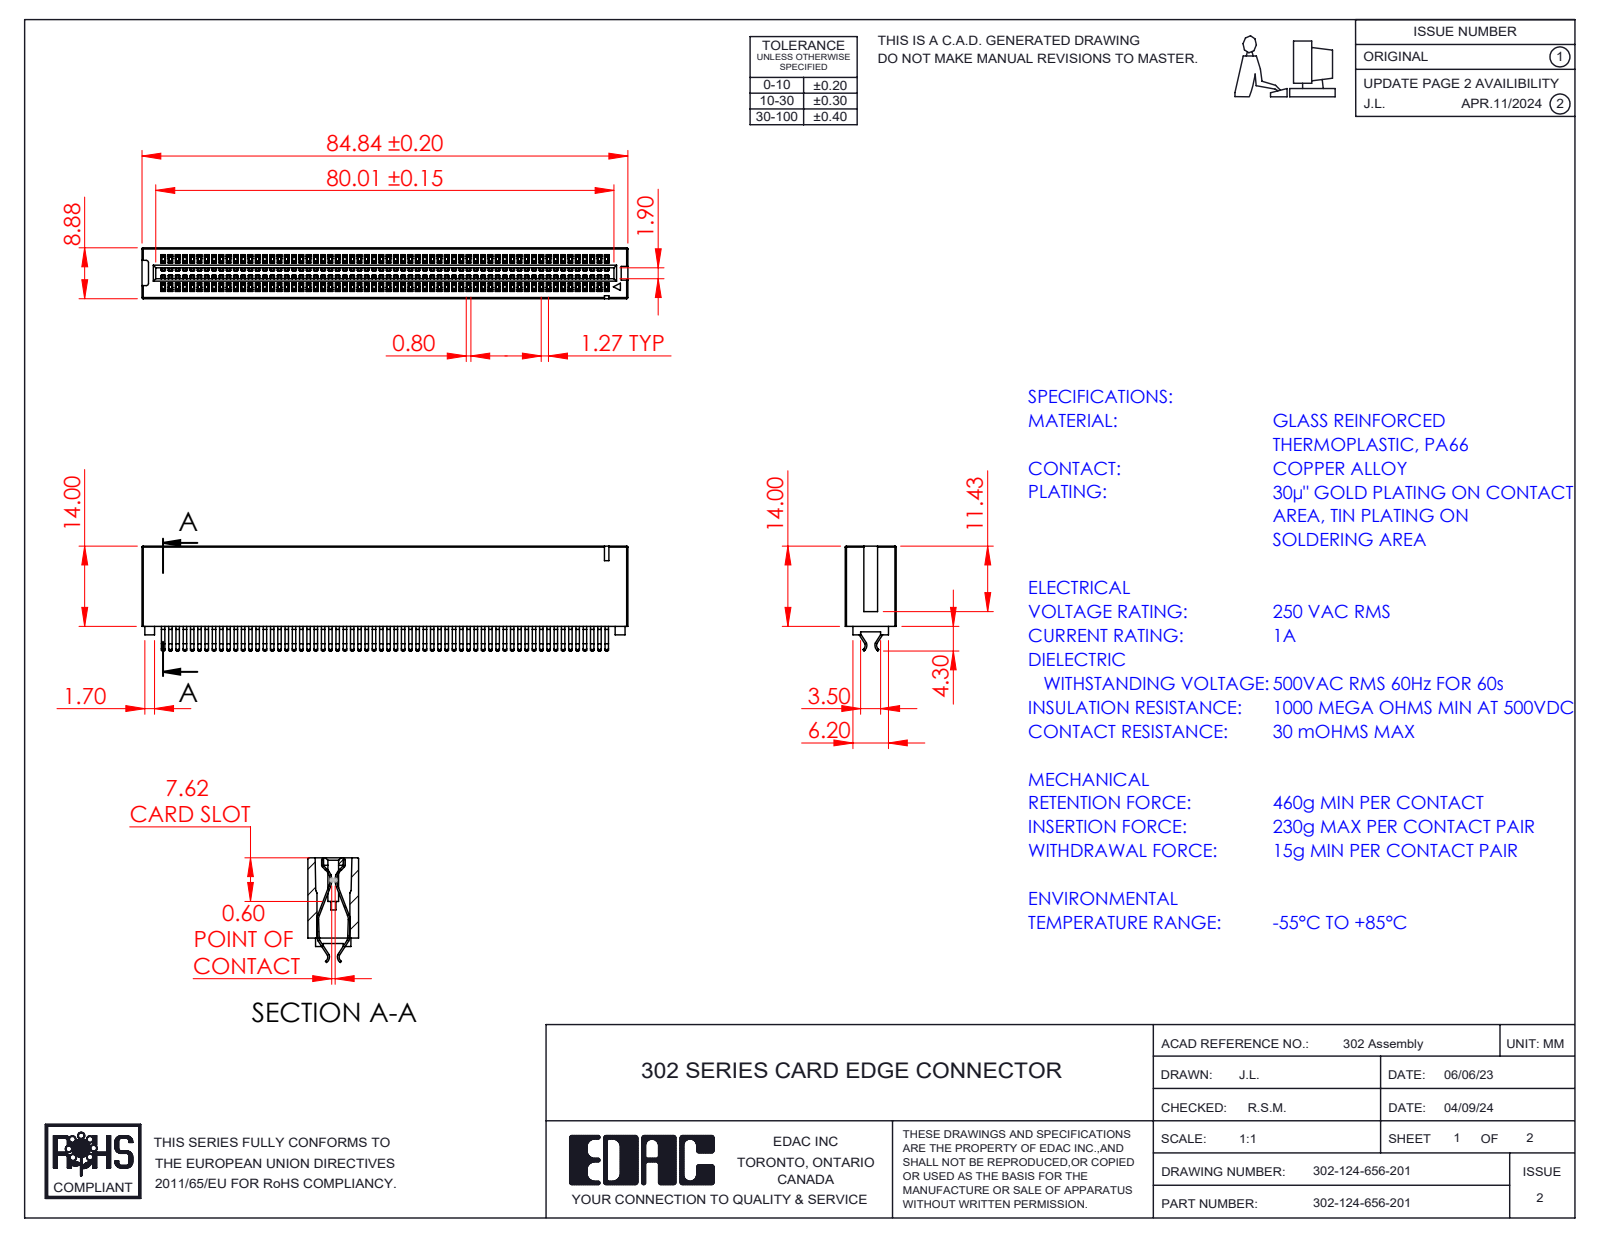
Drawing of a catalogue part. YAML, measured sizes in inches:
part_name: "Contact_302-290-X56; 302-124-656-201; HSG_Vertical HSG"
step_written_by: "SolidWorks 2023 (CONFIG_CONTROL_DESIGN)"
units: inches
bodies: {solids: 125, faces: 5956, planar: 3955, cylindrical: 1997, other: 4}
overall_size: [3.34, 0.72, 0.35]
volume: 0.394
surface_area: 29.01
partial_cylinders:
  - {radius: 0.008, count: 380}
  - {radius: 0.004, count: 2}
  - {radius: 0.016, count: 2}
  - {radius: 0.016, count: 2}
  - {radius: 0.037, count: 2}
  - {radius: 0.041, count: 2}
  - {radius: 0.048, count: 2}
  - {radius: 0.049, count: 2}
face_to_face_distances: [0.35, 0.05, 0.1, 0.15, 0.031, 0.019, 0.075, 0.2, 0.137, 0.212]
